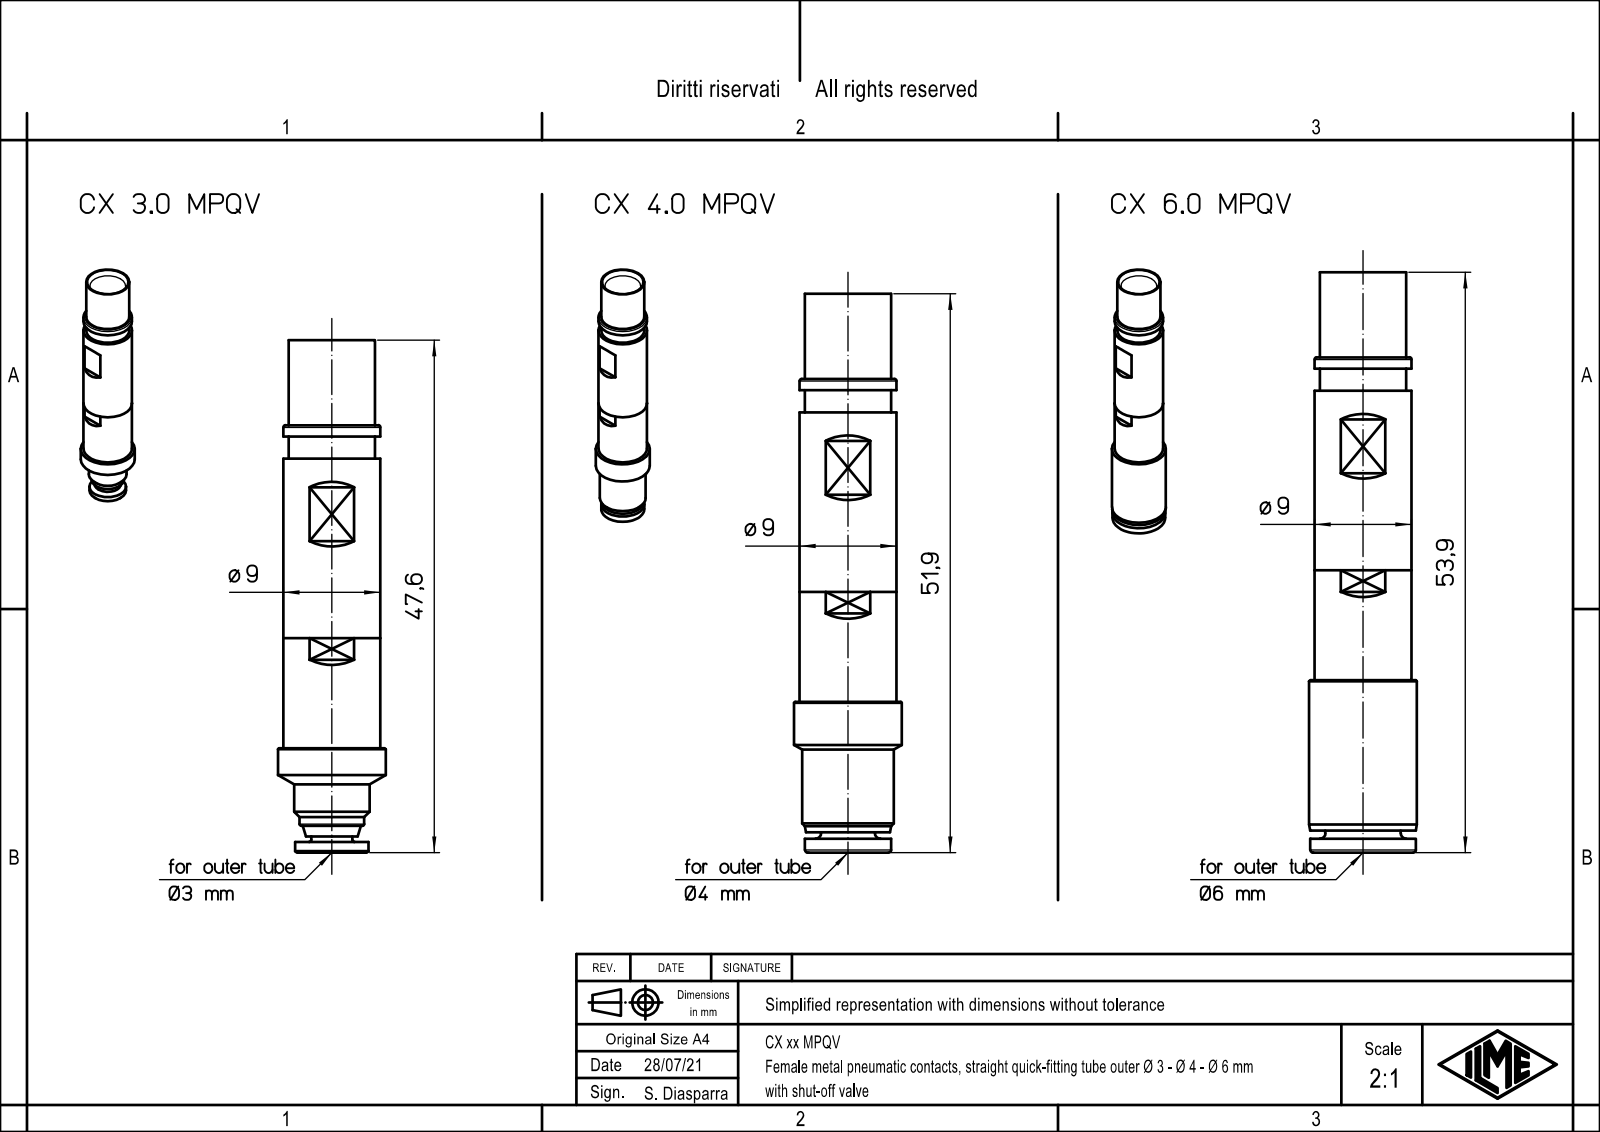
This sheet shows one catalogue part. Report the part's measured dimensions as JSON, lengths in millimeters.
{"part_name": "CX_6.0_MPQV", "step_written_by": "Creo Elements/Direct Modeling 20.1B 02-Apr-2019 (C) Parametric Technology GmbH (AUTOMOTIVE_DESIGN)", "units": "millimeters", "bodies": {"solids": 1, "faces": 136, "planar": 56, "cylindrical": 28, "other": 52}, "overall_size": [53.85, 10, 10], "volume_mm3": 2755, "surface_area_mm2": 2497, "round_holes": [[6.2, 1], [6.6, 1], [7.2, 1]], "round_bosses_or_shafts": [[10, 1], [9.8, 1], [9, 1], [8, 1], [7.8, 1], [7, 1], [4.65, 1]], "partial_cylinders_radius": [[0.24, 1], [0.63, 1]], "face_to_face_distances": [4, 2, 6, 2.05, 42.85, 3.7, 4.3, 1.7, 2.3, 0.6]}
